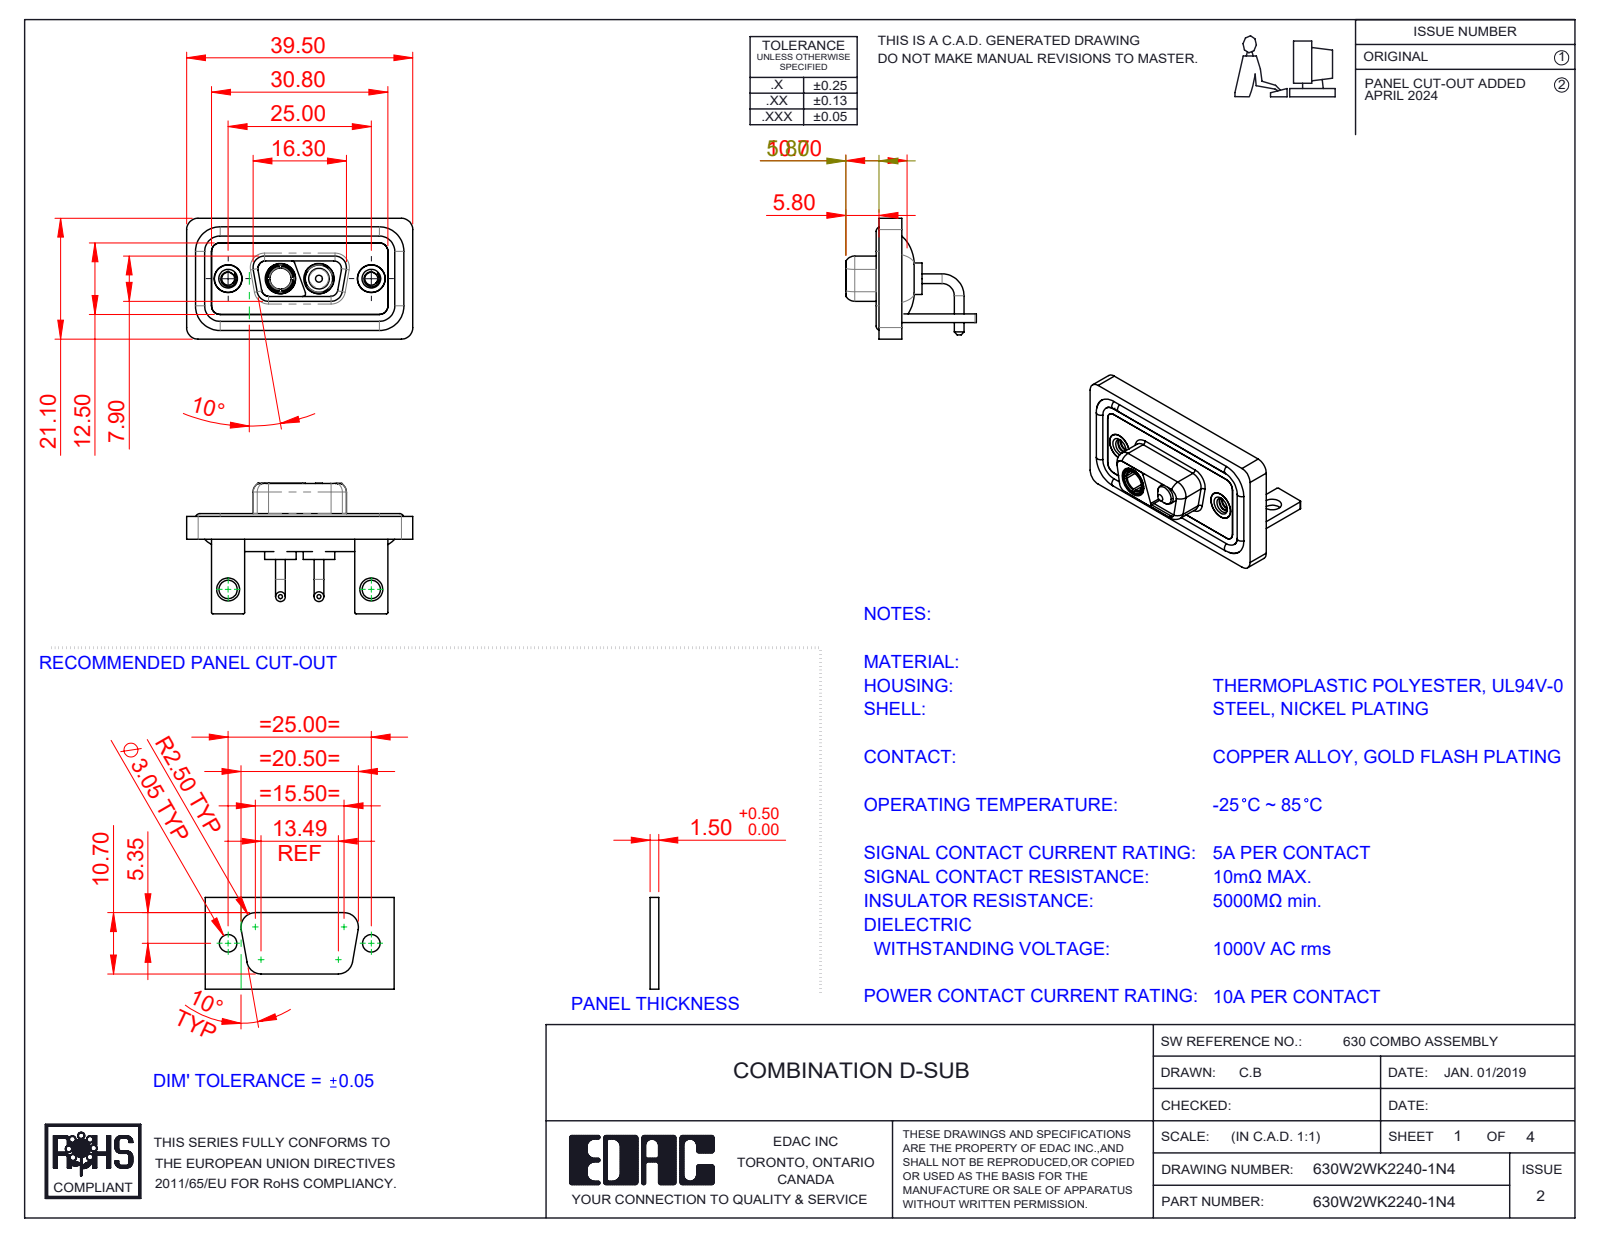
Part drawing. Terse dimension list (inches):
name: 630Combo Housing_2WK2; 630W2WK2240-1N4; 630Combo Shell Rear_09 Contacts; 630Combo Threaded Rivet_2 (+5 more)
written by: SolidWorks 2023 (CONFIG_CONTROL_DESIGN)
unit: in
bodies: 13 solids, 556 faces (164 planar, 259 cylindrical, 133 other)
size: 1.555 × 0.898 × 0.831
volume: 0.302 in³; area: 12.6 in²
holes: 4× ⌀0.191, 2× ⌀0.089, 2× ⌀0.126, 2× ⌀0.157, 2× ⌀0.159, 2× ⌀0.197, 2× ⌀0.209, 1× ⌀0.146
bosses: 4× ⌀0.067, 4× ⌀0.063, 2× ⌀0.217, 2× ⌀0.205, 2× ⌀0.195, 2× ⌀0.189, 2× ⌀0.187, 2× ⌀0.148
rounds: 19× R0.079, 18× R0.059, 16× R0.01, 8× R0.053, 8× R0.063, 7× R0.02, 4× R0.024, 4× R0.026
face distances: 0.016, 0.114, 0.059, 0.043, 0.146, 0.071, 0.031, 0.098, 0.063, 0.122
hole spacings: 0.36, 0.624, 0.984, 0.265
